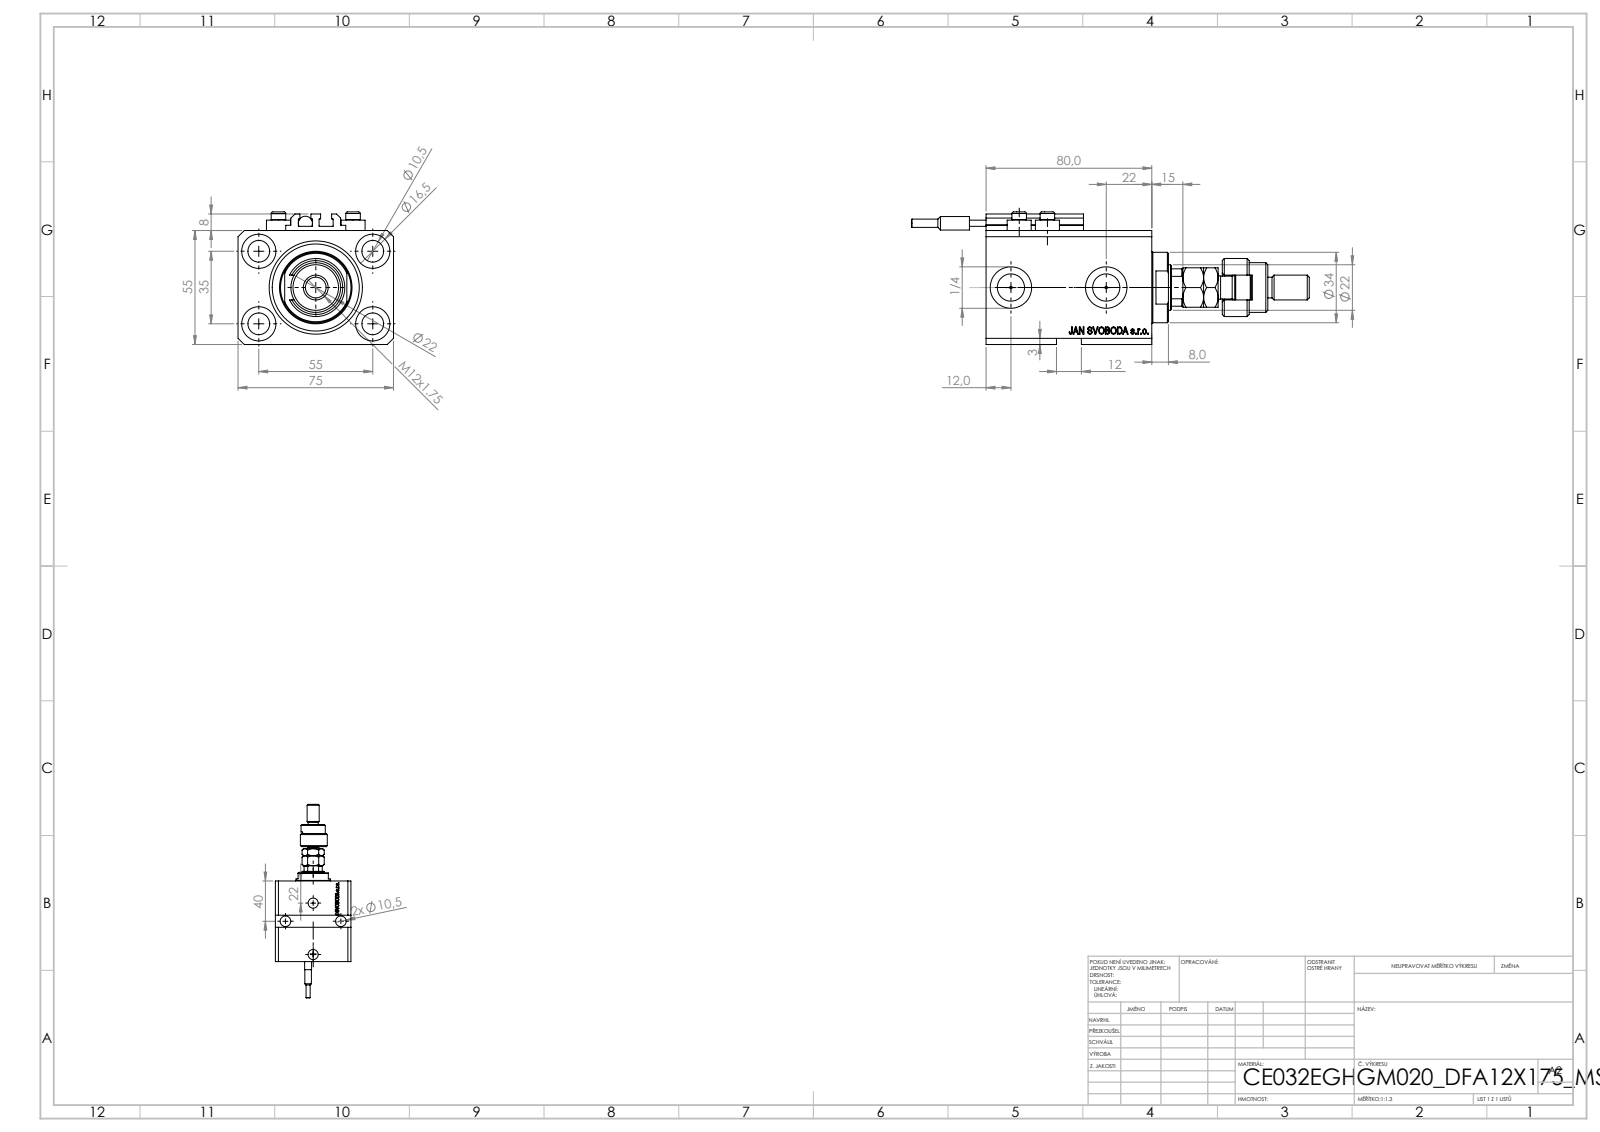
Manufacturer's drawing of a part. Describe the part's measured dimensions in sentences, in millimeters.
The part is named "V250CE_E_Body; ALLEN BOLT V250CE; MFA; SWITCH_V250CE (+3 more)". Its 3-D file was written by "SolidWorks 2019 (CONFIG_CONTROL_DESIGN)". It is 11 solids with 1175 faces: 558 planar, 145 cylindrical and 472 other. Overall it measures 192 by 75 by 64 millimeters. Its volume is 303 561 cubic millimeters and its surface area 82 960 square millimeters. Round holes: 7 of diameter 10.5, 4 of diameter 1.25, 4 of diameter 4, 4 of diameter 16.5, 2 of diameter 10, 2 of diameter 13.16, 2 of diameter 20, 1 of diameter 22, 1 of diameter 32, 1 of diameter 45. Round bosses or shafts: 4 of diameter 11.6, 4 of diameter 7, 1 of diameter 34, 1 of diameter 28, 1 of diameter 24, 1 of diameter 18, 1 of diameter 12, 1 of diameter 11. Partial cylindrical surfaces (rounded edges, fillets, slot ends): 10 of radius 0.2, 1 of radius 9.75, 1 of radius 10.5. The main face-to-face distances are 55, 75, 15, 80, 3, 65, 55.1, 9.9, 70.1, 54. The hole center spacings are 32.6, 55, 13.6, 14.09, 19.89, 20.12, 25.81, 28.48.
